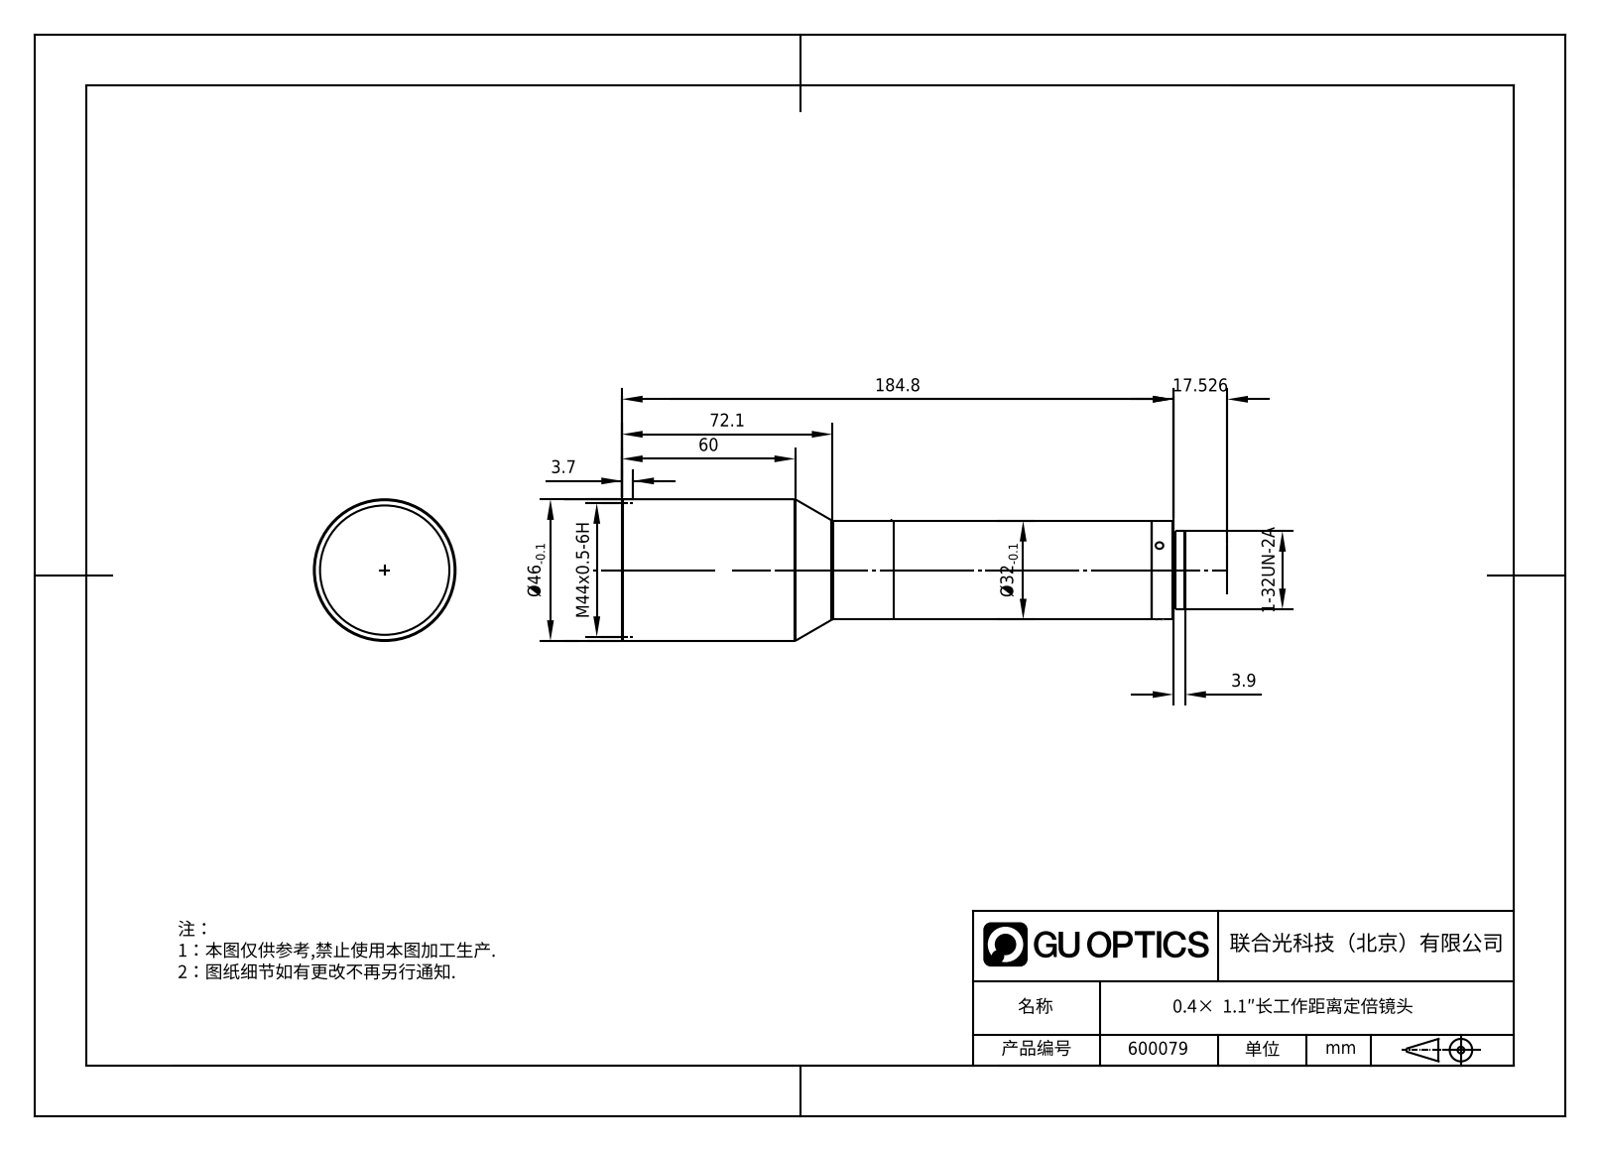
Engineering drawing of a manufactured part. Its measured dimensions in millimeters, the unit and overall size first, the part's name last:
Units: millimetres
Overall size (bounding box): 188.7 × 46 × 46
Round holes (diameter × count): ⌀2.5 ×3, ⌀42 ×1
Round bosses / shafts (diameter × count): ⌀46 ×1, ⌀32 ×1, ⌀25.4 ×1, ⌀24.6 ×1
Partial cylindrical surfaces — rounded edges, fillets, slot ends (radius × count): R14.86 ×1
Main face-to-face distances: 3.9, 188.7, 184.8, 3.1, 0.8, 185.6
Volume: 200 915 mm³ · Surface area: 25 872 mm²
Bodies: 1 solid, 25 faces (4 planar, 12 cylindrical, 9 other)
Part name (STEP PRODUCT): 600079
STEP written by: SolidWorks 2020 (AUTOMOTIVE_DESIGN)
